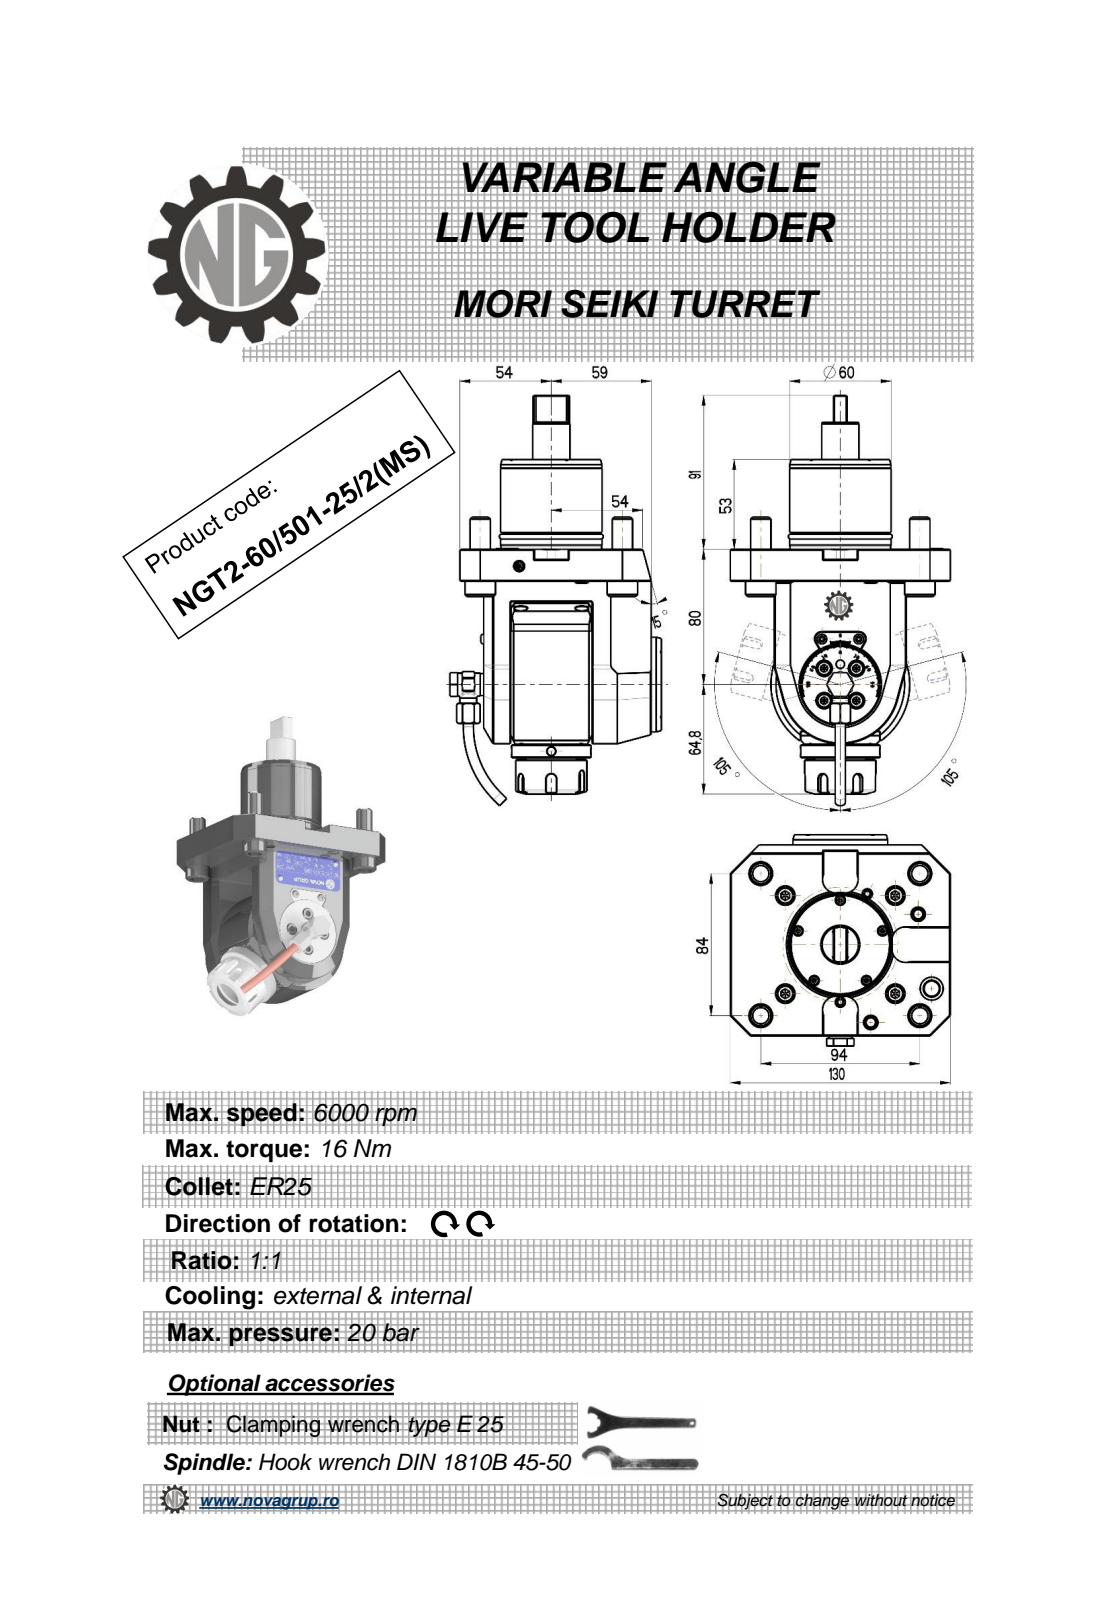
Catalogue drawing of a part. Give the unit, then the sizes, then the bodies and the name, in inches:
Units: inches
Overall size (bounding box): 9.554 × 5.118 × 4.917
Round holes (diameter × count): ⌀0.157 ×3, ⌀0.197 ×2, ⌀0.354 ×2, ⌀0.118 ×1, ⌀0.244 ×1, ⌀0.394 ×1, ⌀0.433 ×1, ⌀0.799 ×1
Round bosses / shafts (diameter × count): ⌀0.709 ×4, ⌀0.472 ×4, ⌀0.315 ×2, ⌀0.236 ×2, ⌀0.224 ×2, ⌀2.362 ×1, ⌀2.354 ×1, ⌀2.339 ×1
Partial cylindrical surfaces — rounded edges, fillets, slot ends (radius × count): R0.014 ×20, R0.016 ×12, R0.004 ×10, R0.118 ×10, R0.315 ×6, R0.108 ×5, R0.02 ×4, R0.031 ×2
Main face-to-face distances: 0.748, 0.236, 0.472, 1.22, 1.024, 4.094, 3.071, 3.898, 0.551, 2.835
Hole centre spacings: 0.016, 1.553, 1.929, 1.945, 2.311, 2.317, 2.359
Volume: 68.1 in³ · Surface area: 166.7 in²
Bodies: 2 solids, 650 faces (265 planar, 199 cylindrical, 186 other)
Part name (STEP PRODUCT): NGT2_60_501_25_2_MS
STEP written by: PRO/ENGINEER BY PARAMETRIC TECHNOLOGY CORPORATION, 2010280 (CONFIG_CONTROL_DESIGN)
